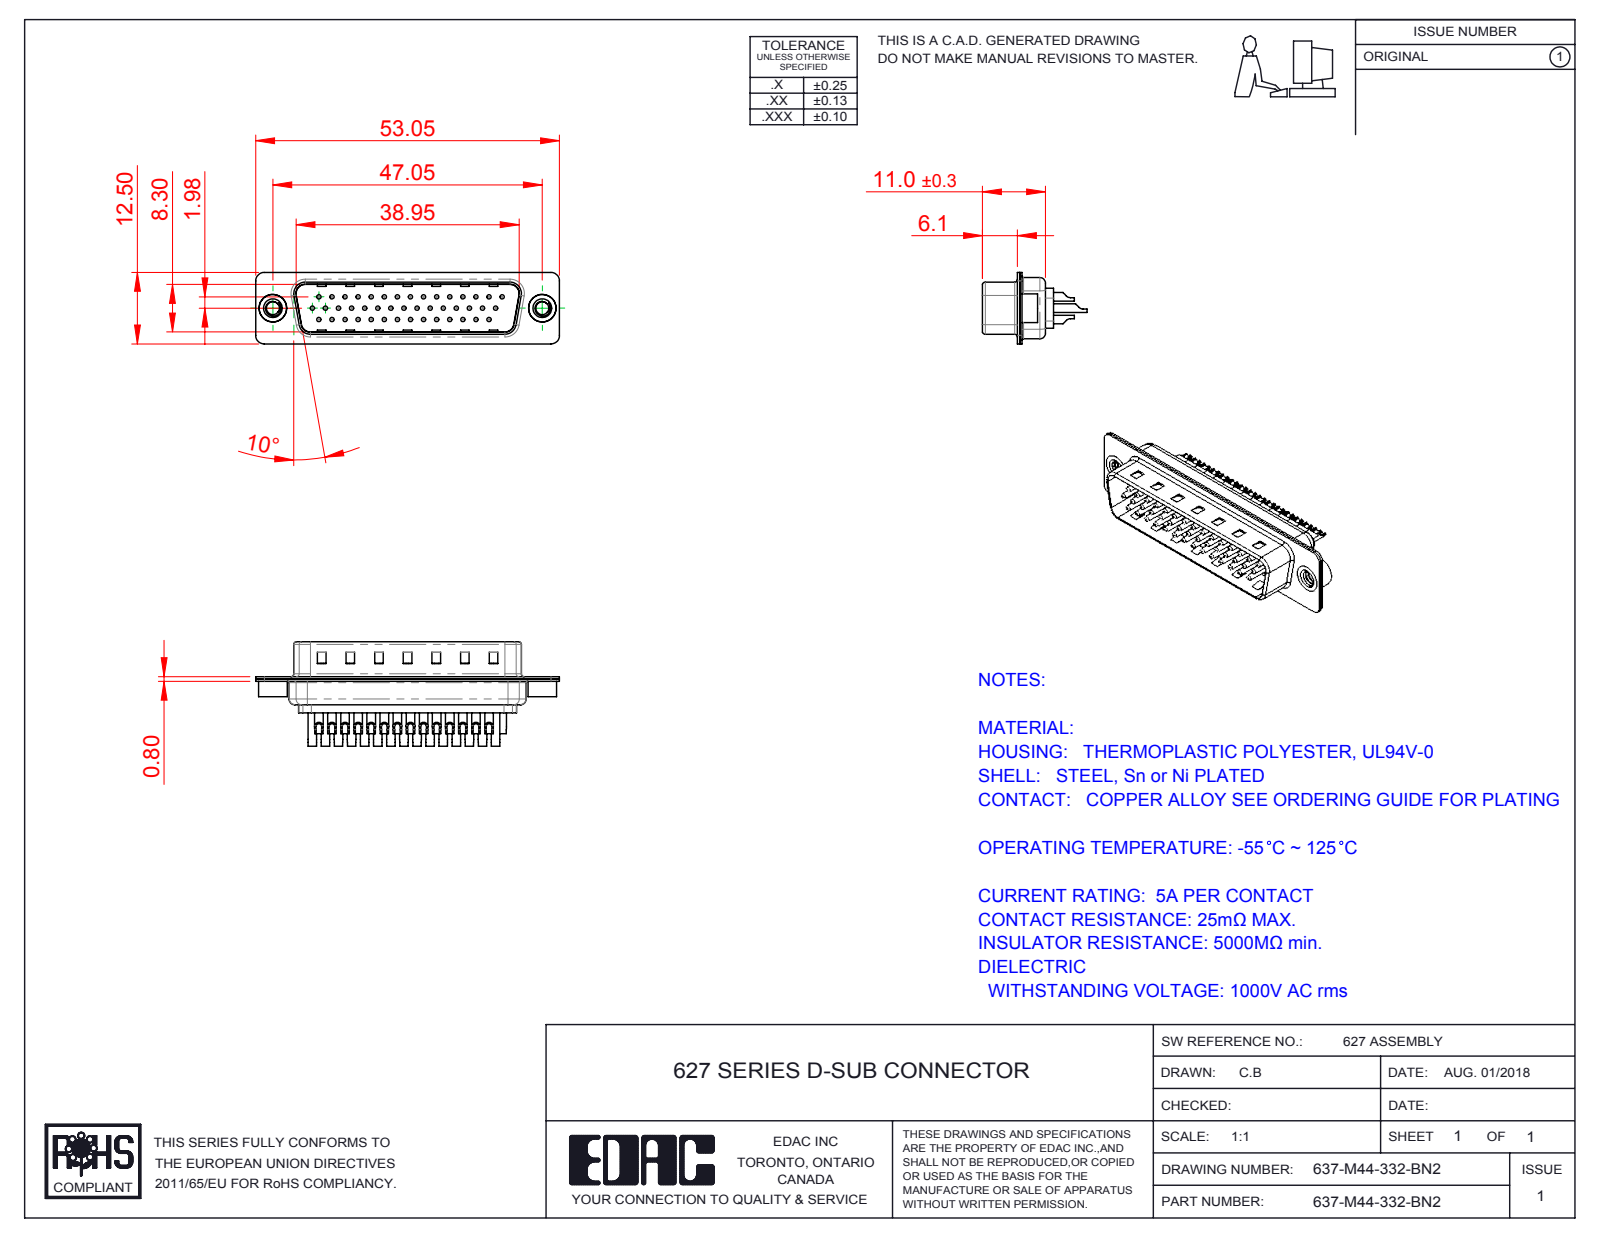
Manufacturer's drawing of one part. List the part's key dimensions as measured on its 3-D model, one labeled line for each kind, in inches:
Part name (STEP PRODUCT): 637M Shell Rear_44 Contacts; 637-M44-332-BN2; 637M Housing_44 Contacts; 637M Contact Row 2_32 (+4 more)
STEP written by: SolidWorks 2016 (CONFIG_CONTROL_DESIGN)
Units: inches
Bodies: 49 solids, 2004 faces (567 planar, 841 cylindrical, 596 other)
Overall size (bounding box): 2.089 × 0.719 × 0.492
Volume: 0.181 in³ · Surface area: 13.97 in²
Round holes (diameter × count): ⌀0.03 ×44, ⌀0.039 ×44, ⌀0.063 ×44, ⌀0.079 ×44, ⌀0.089 ×2, ⌀0.157 ×2, ⌀0.189 ×2
Round bosses / shafts (diameter × count): ⌀0.059 ×44, ⌀0.079 ×3, ⌀0.03 ×3, ⌀0.197 ×2, ⌀0.193 ×2
Partial cylindrical surfaces — rounded edges, fillets, slot ends (radius × count): R0.059 ×16, R0.079 ×12, R0.02 ×8, R0.063 ×8, R0.039 ×7, R0.01 ×4, R0.024 ×4, R0.026 ×4
Main face-to-face distances: 0.016, 0.031, 0.374, 0.358, 0.343, 0.39, 0.03, 0.014, 0.043, 0.047
Hole centre spacings: 0.09, 0.156, 0.09, 0.18, 0.324, 0.27, 0.45, 0.59
